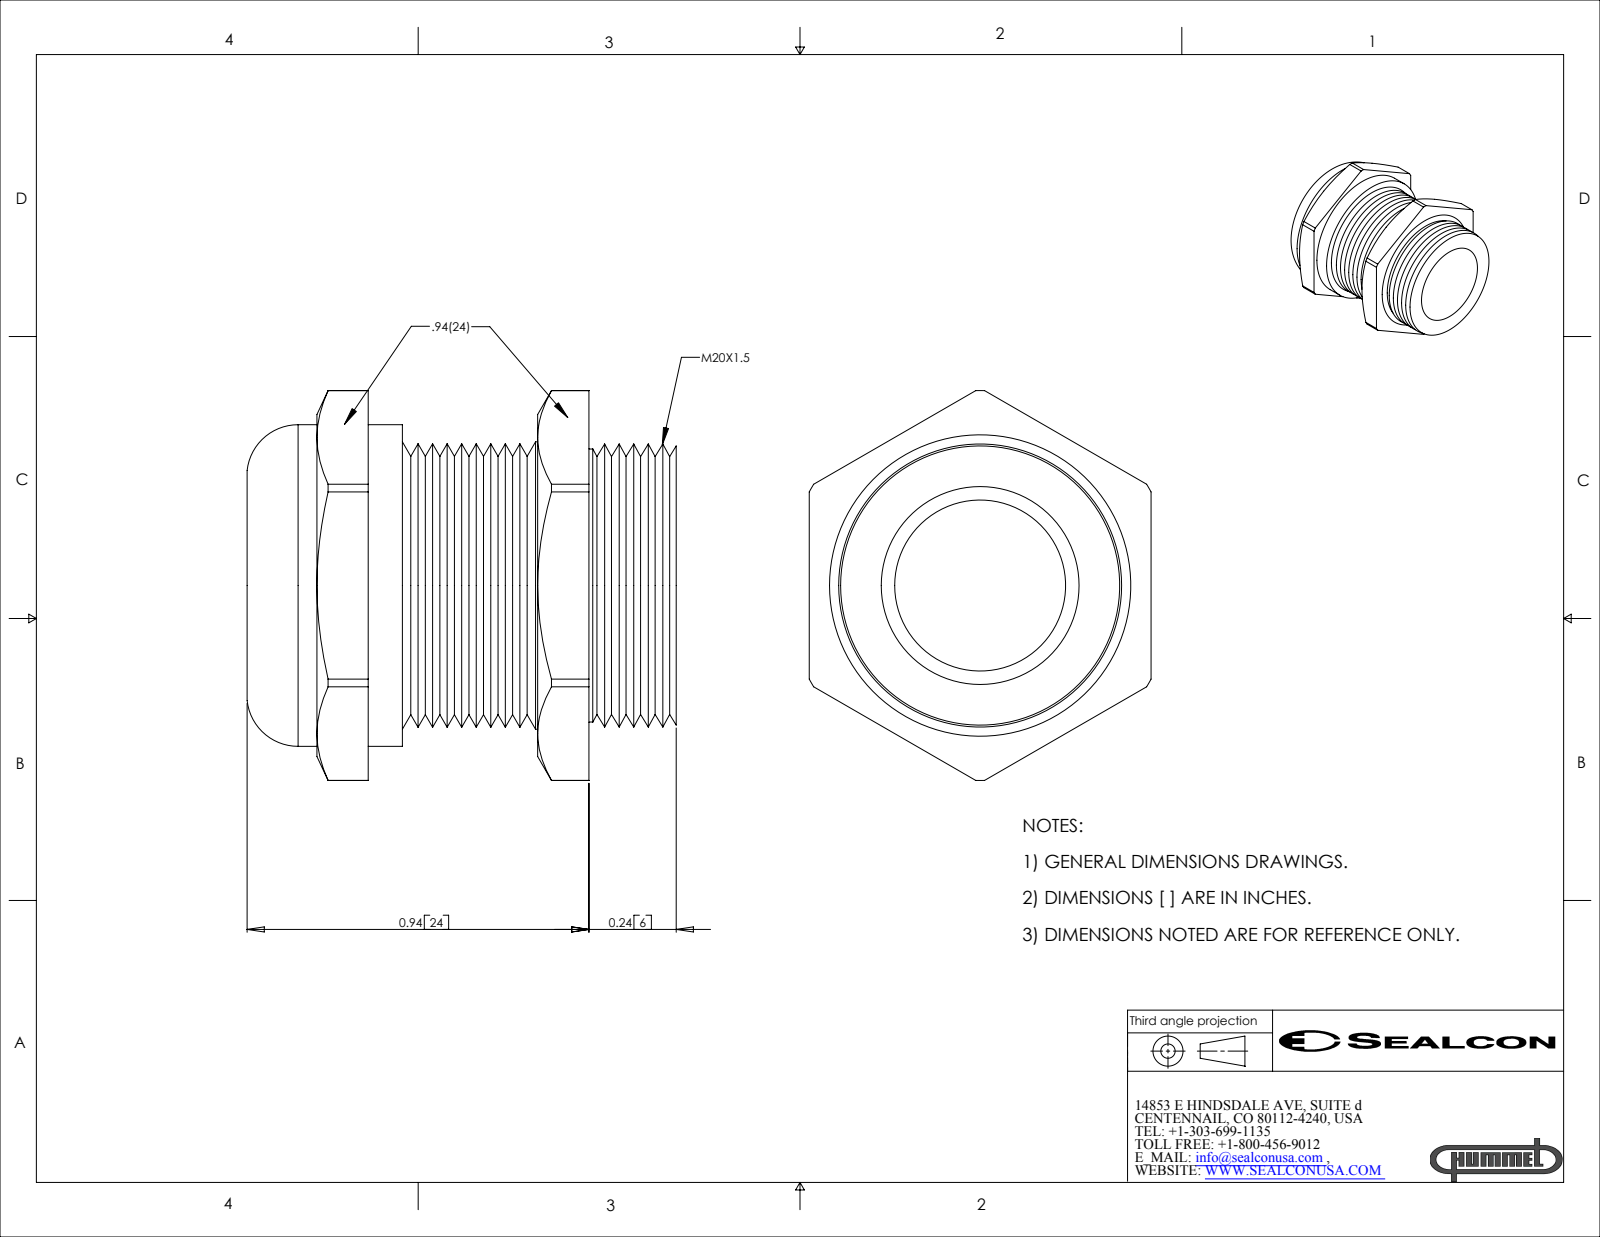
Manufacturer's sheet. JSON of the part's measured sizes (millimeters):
{"part_name": "CD22MR-BR", "step_written_by": "SolidWorks 2007 (CONFIG_CONTROL_DESIGN)", "units": "millimeters", "bodies": {"solids": 2, "faces": 129, "planar": 21, "cylindrical": 26, "other": 82}, "overall_size": [30, 27.2, 23.9], "volume_mm3": 6780, "surface_area_mm2": 5714, "round_holes": [[11.9, 1], [16.1, 1]], "round_bosses_or_shafts": [[22.5, 1], [20.1, 1]], "partial_cylinders_radius": [[13.6, 1]], "face_to_face_distances": [23.9, 3.6, 15.4, 25.1, 19, 6.1, 9.7, 11.8, 21.5, 6]}
